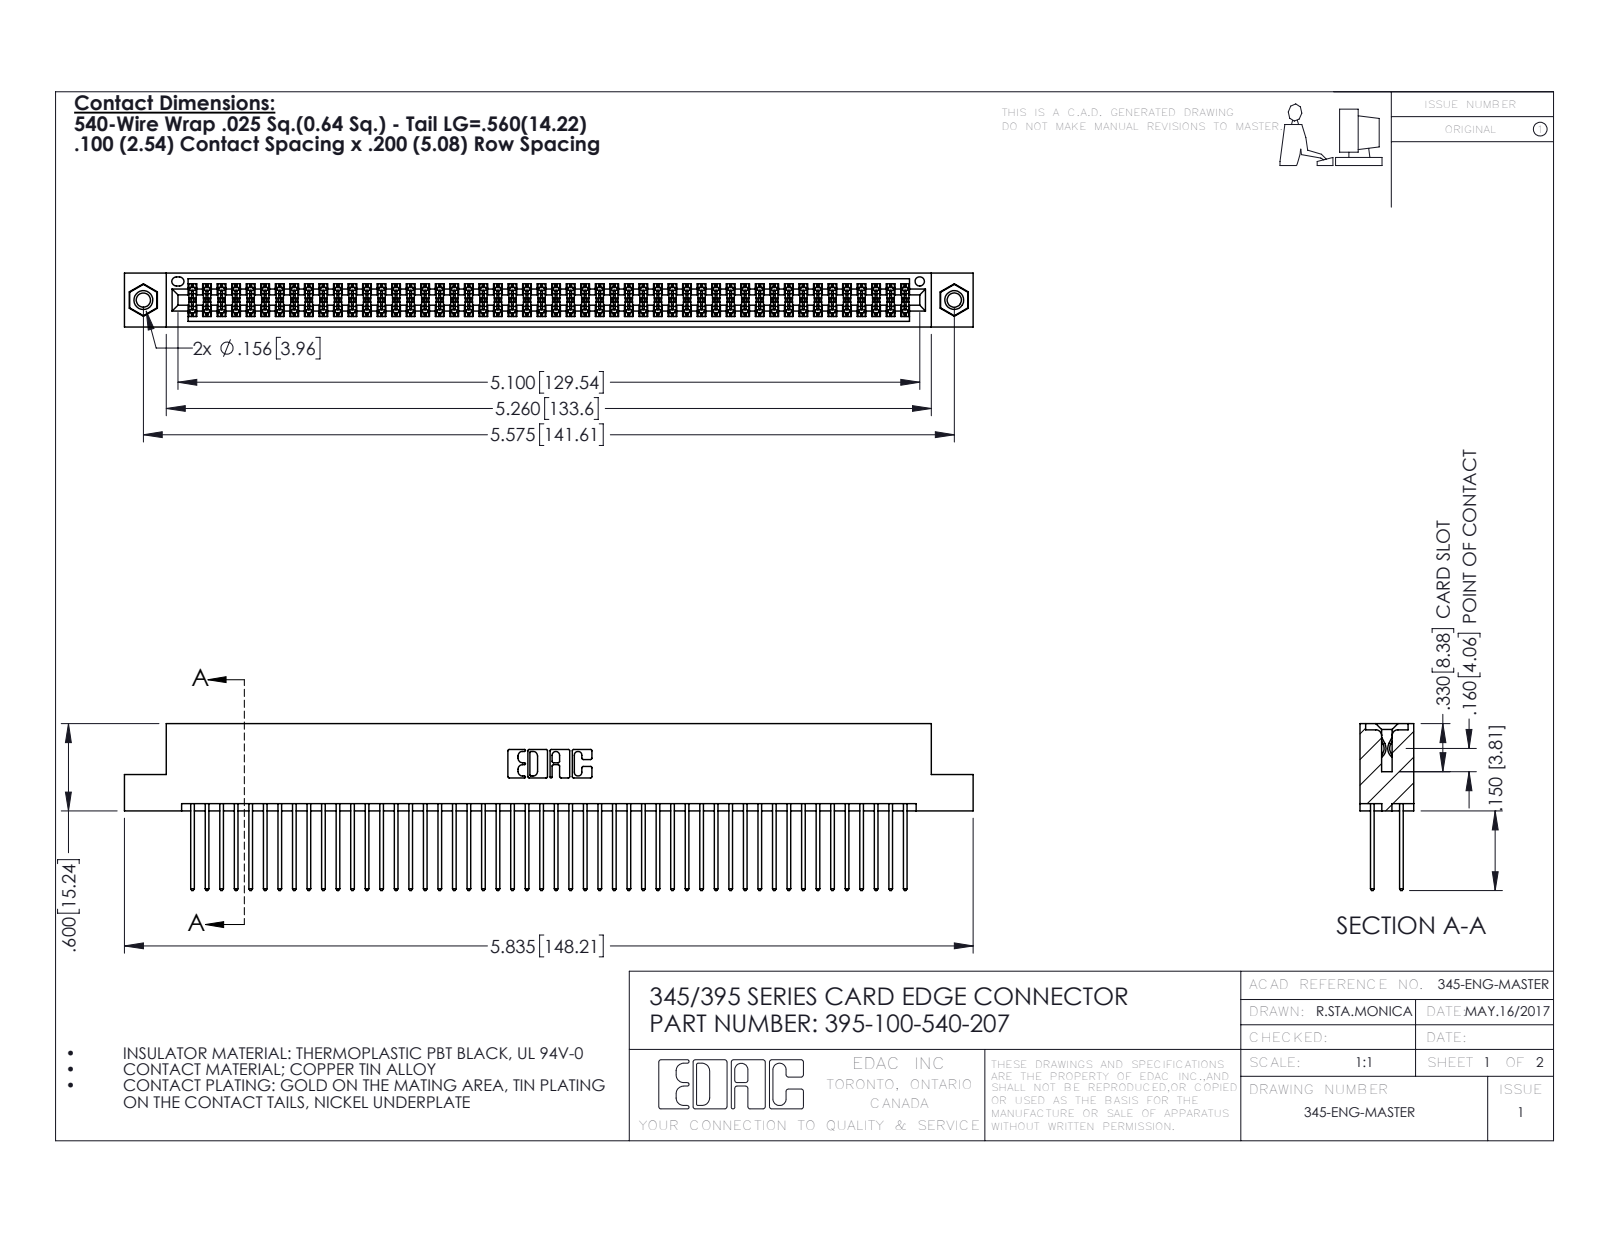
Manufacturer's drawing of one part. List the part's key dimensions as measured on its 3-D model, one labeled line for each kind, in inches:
Part name (STEP PRODUCT): 345-292-001_345-293-140; 345 Part_Flush Mounting Lugs - 0.156 Dia-TI; 395-100-540-207; 345-250-001_345-250-005-103
STEP written by: SolidWorks 2016 (CONFIG_CONTROL_DESIGN)
Units: inches
Bodies: 103 solids, 5186 faces (3412 planar, 1758 cylindrical, 16 other)
Overall size (bounding box): 5.835 × 1.147 × 0.37
Volume: 0.905 in³ · Surface area: 37 in²
Round holes (diameter × count): ⌀0.098 ×2, ⌀0.125 ×2, ⌀0.156 ×2, ⌀0.064 ×1
Round bosses / shafts (diameter × count): ⌀0.155 ×2
Partial cylindrical surfaces — rounded edges, fillets, slot ends (radius × count): R0.006 ×150, R0.01 ×100, R0.01 ×22, R0.007 ×6, R0.031 ×6, R0.026 ×3, R0.014 ×2, R0.019 ×2
Main face-to-face distances: 0.072, 0.298, 0.2, 0.098, 0.272, 0.025, 0.37, 0.225, 0.175, 0.149
Hole centre spacings: 0.27, 5.339, 5.575
